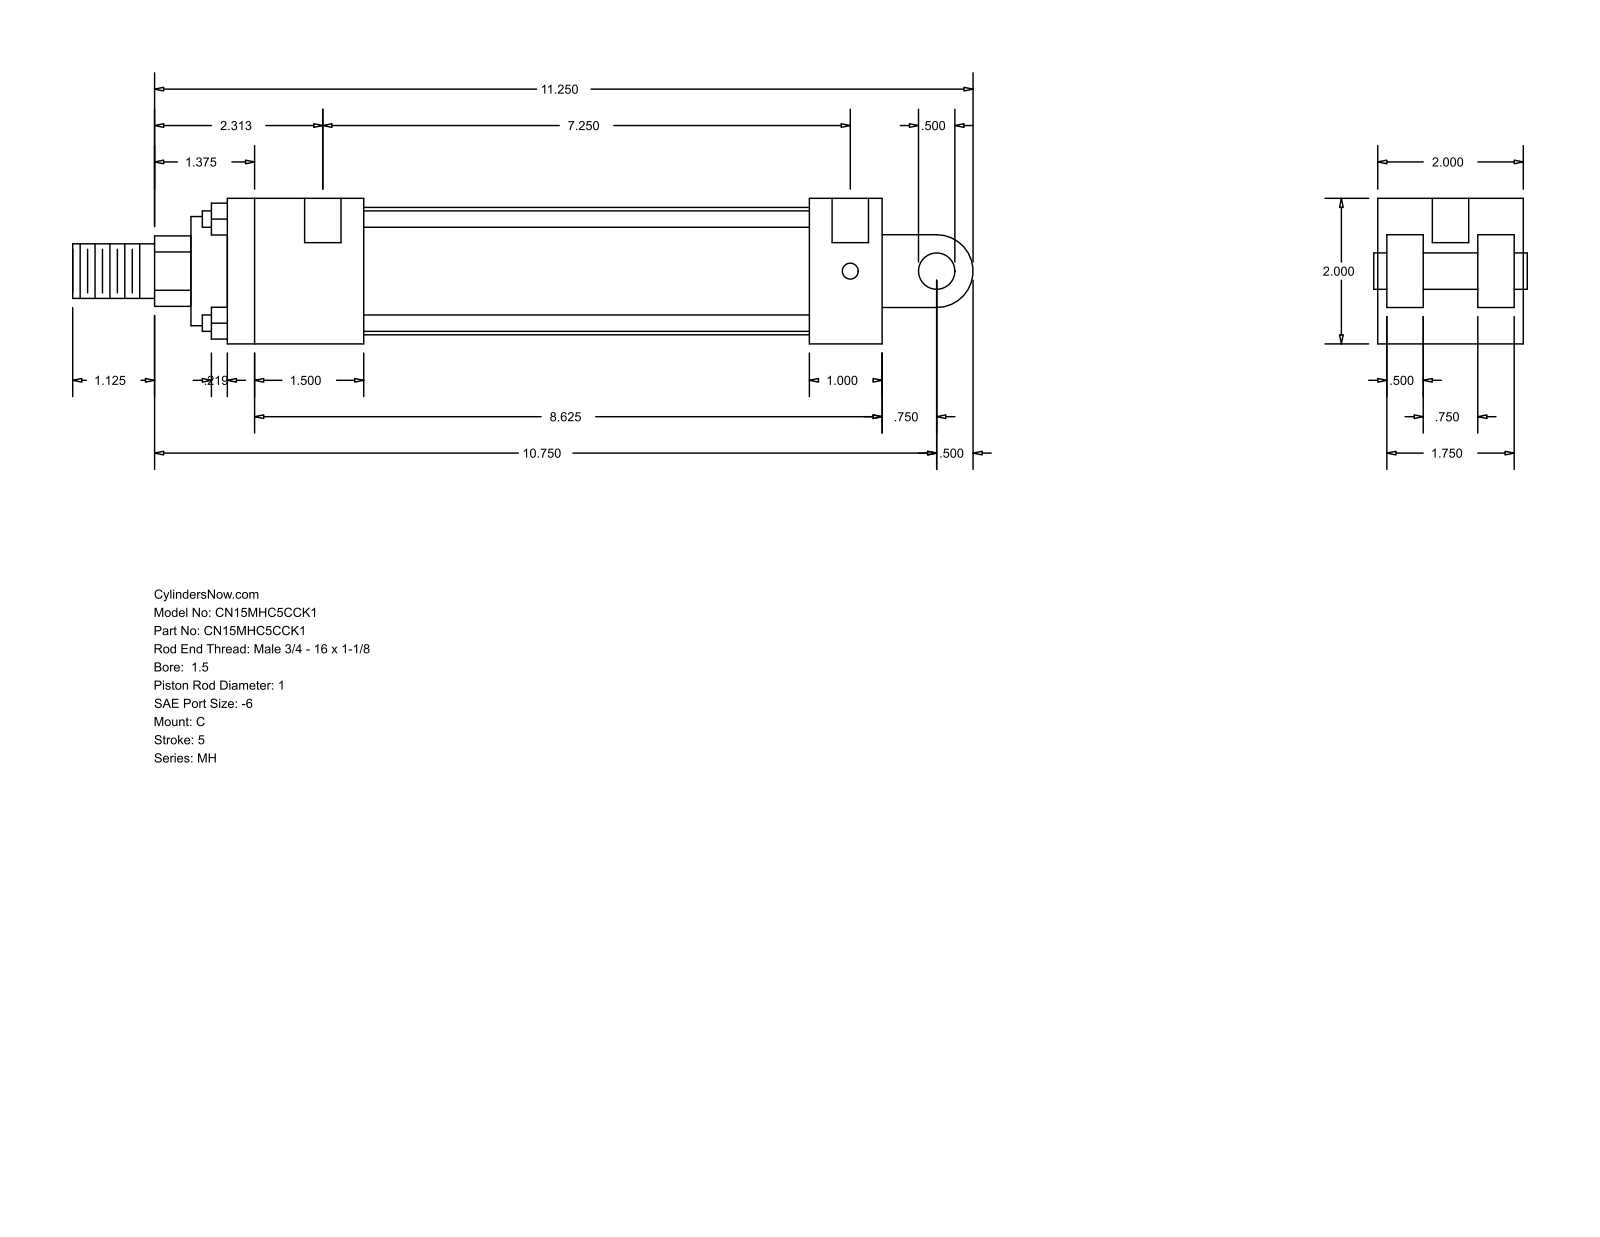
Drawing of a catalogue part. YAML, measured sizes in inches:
part_name: "MH_C__0150_1"
step_written_by: "GSSL Pune (CONFIG_CONTROL_DESIGN)"
units: inches
bodies: {solids: 0, faces: 99, planar: 70, cylindrical: 29, other: 0}
overall_size: [12.375, 2, 2]
round_holes:
  - {diameter: 0.219, count: 4}
  - {diameter: 0.5, count: 2}
round_bosses_or_shafts:
  - {diameter: 0.225, count: 4}
  - {diameter: 1.75, count: 1}
  - {diameter: 1.5, count: 1}
  - {diameter: 1, count: 1}
  - {diameter: 0.75, count: 1}
  - {diameter: 0.5, count: 1}
partial_cylinders:
  - {radius: 0.484, count: 1}
  - {radius: 0.5, count: 1}
face_to_face_distances: [2, 0.5, 1.875, 1, 0.125, 0.625, 1.375, 1.25, 9, 1.5]
hole_center_spacings: [7.375, 0.125, 7.25]
